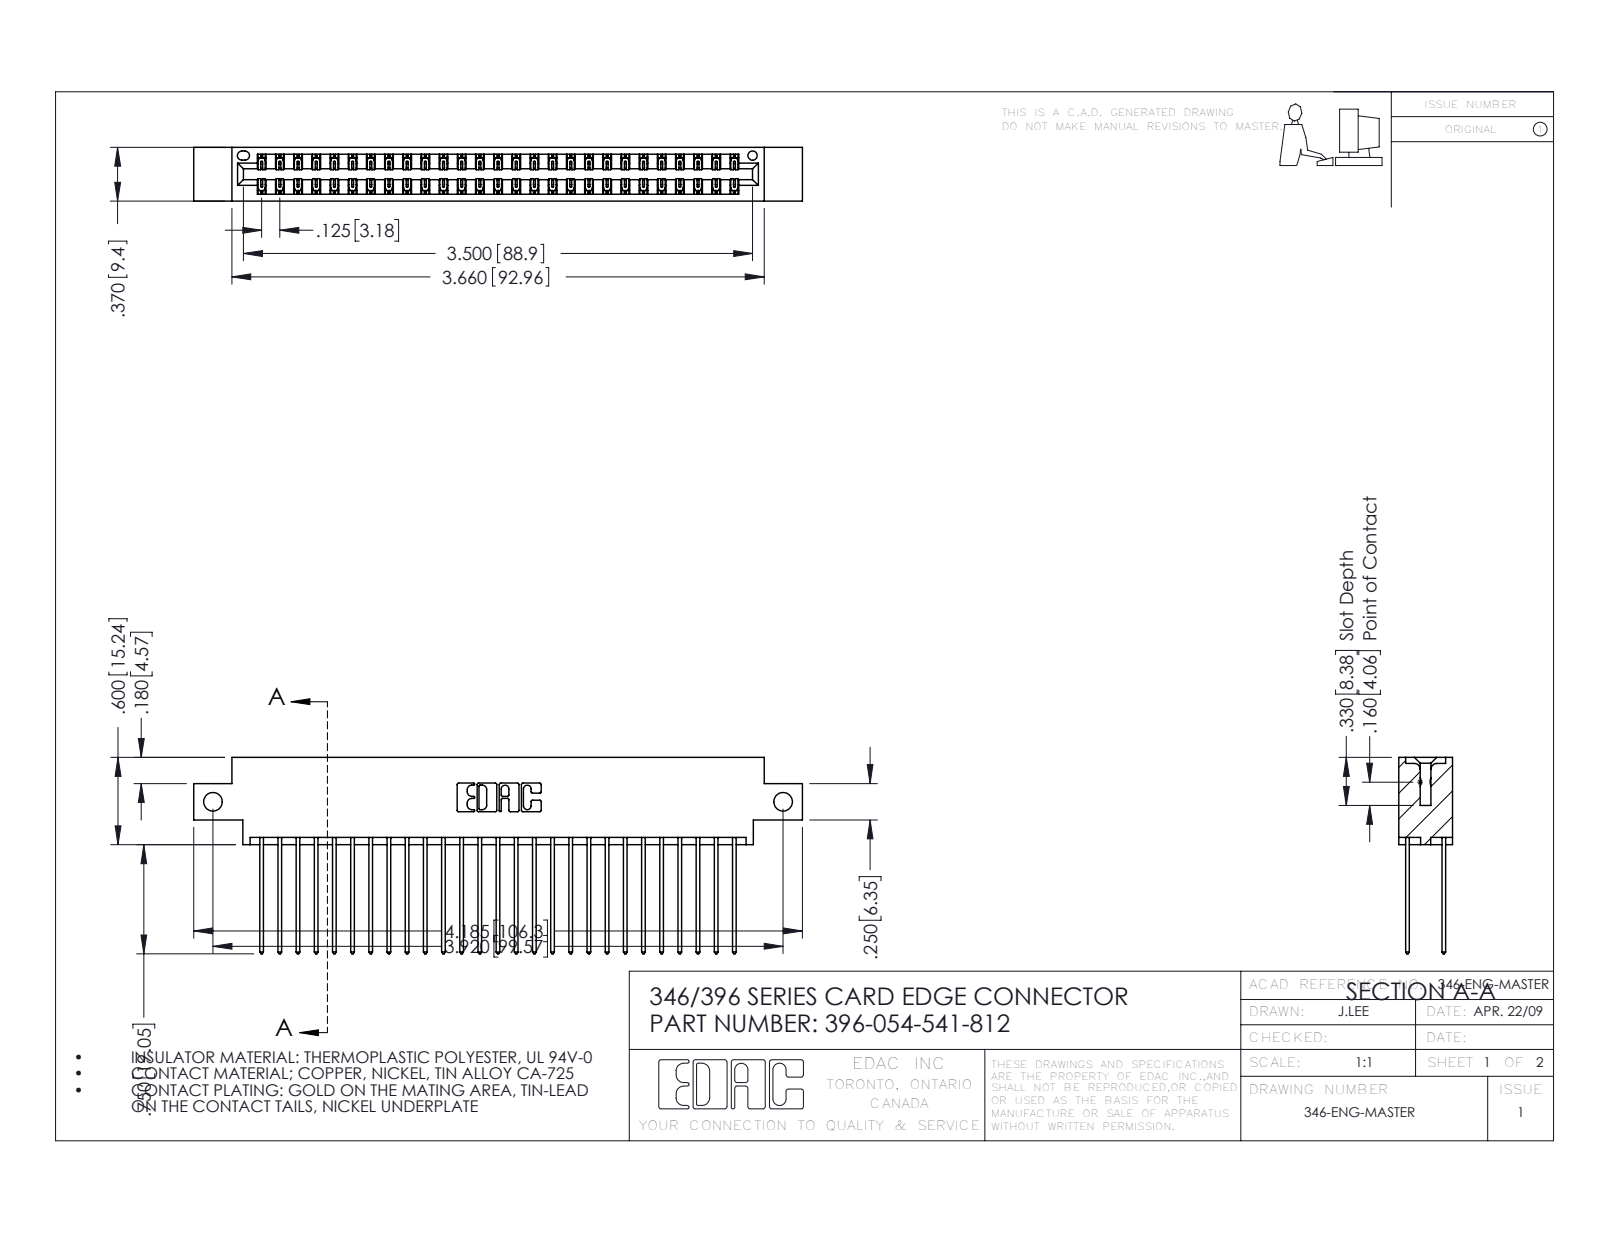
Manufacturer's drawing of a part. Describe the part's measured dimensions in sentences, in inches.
The part is named "346 Part_0.170 Offset - Side Mount; 396-054-541-812; 345-292-001_345-293-141". Its 3-D file was written by "SolidWorks 2016 (CONFIG_CONTROL_DESIGN)". It is 55 solids with 2934 faces: 1970 planar, 964 cylindrical and 0 other. Overall it measures 4.185 by 1.35 by 0.37 inches. Its volume is 0.63 cubic inches and its surface area 23.98 square inches. Round holes: 2 of diameter 0.128, 1 of diameter 0.064. Partial cylindrical surfaces (rounded edges, fillets, slot ends): 81 of radius 0.006, 54 of radius 0.01, 22 of radius 0.01, 6 of radius 0.007, 6 of radius 0.031, 3 of radius 0.026, 2 of radius 0.014, 2 of radius 0.022. The main face-to-face distances are 0.048, 0.322, 0.25, 0.072, 0.298, 0.025, 0.37, 0.275, 0.225, 0.148. The hole center spacings are 3.92.
